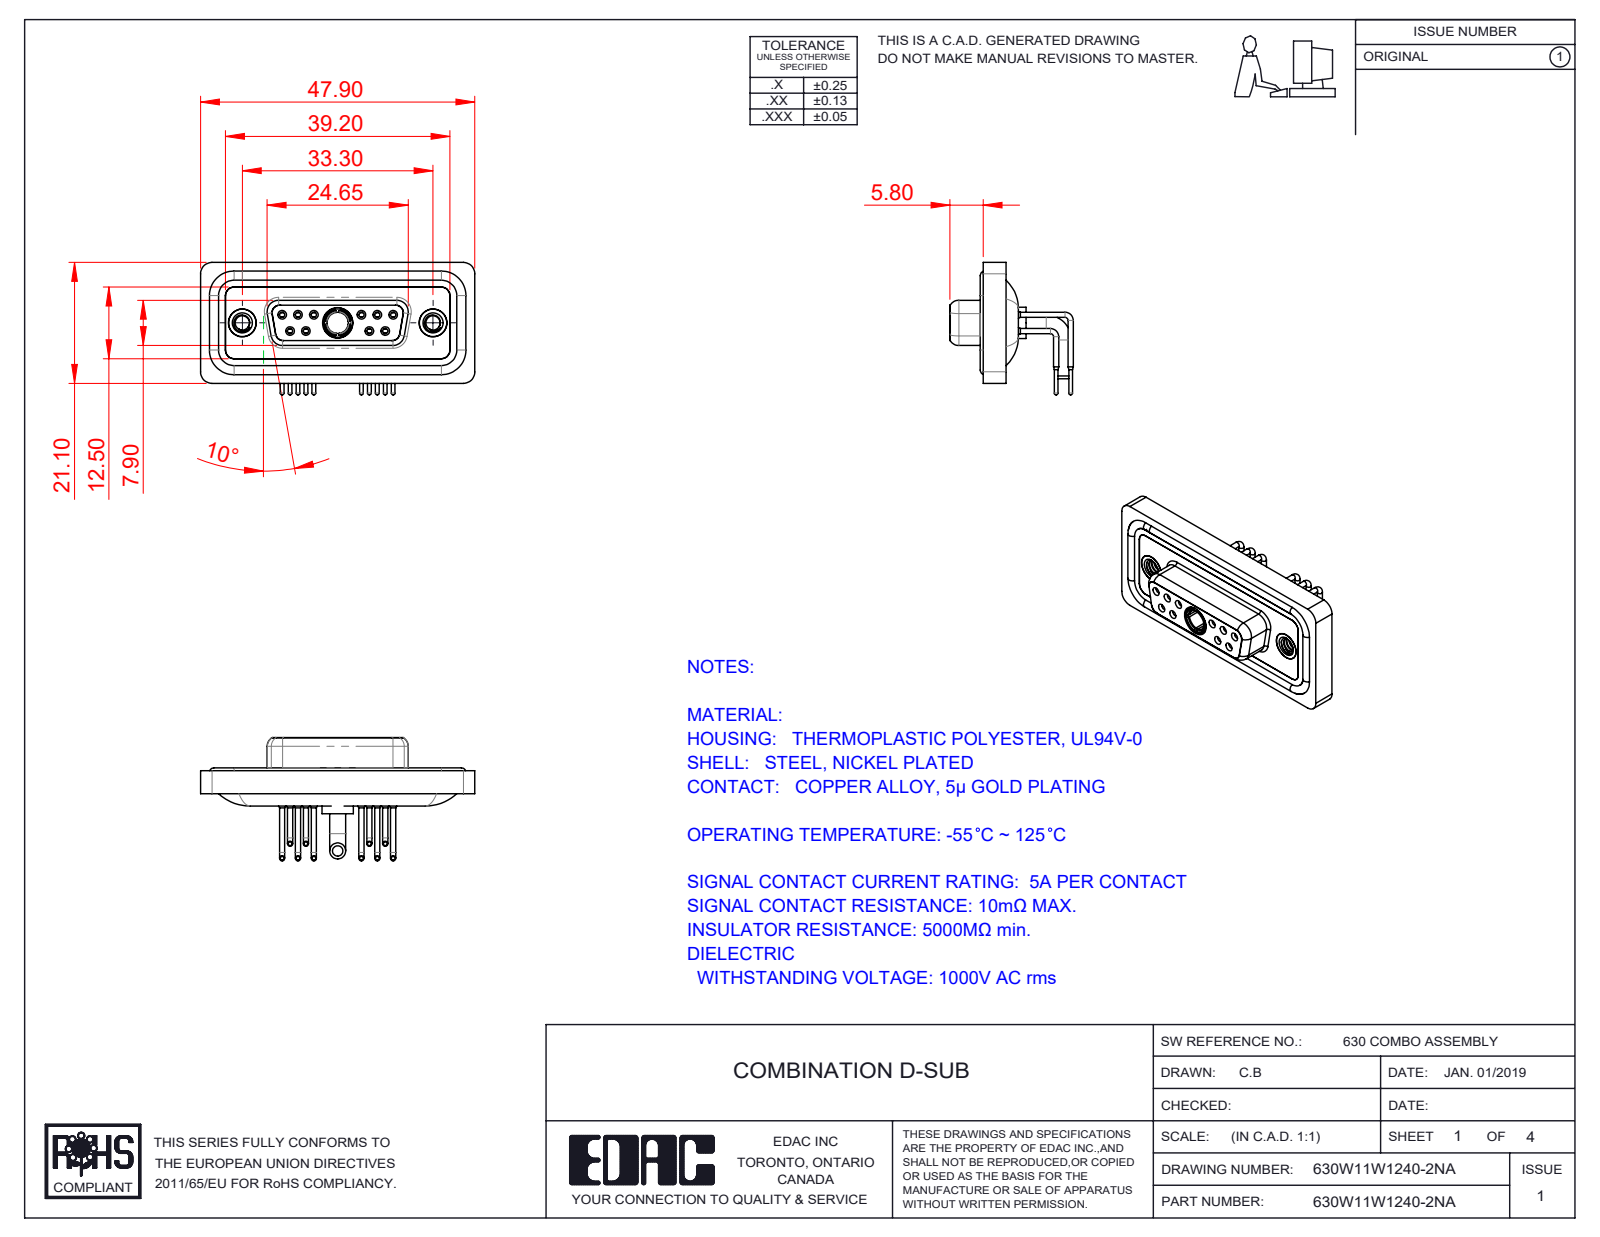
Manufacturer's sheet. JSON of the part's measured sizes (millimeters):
{"part_name": "630Combo Shell Front_15 Contacts; Power Socket_20A RA; 630W11W1240-2NA; 630Combo Shell Rear_15 Contacts (+5 more)", "step_written_by": "SolidWorks 2020 (CONFIG_CONTROL_DESIGN)", "units": "millimeters", "bodies": {"solids": 19, "faces": 988, "planar": 284, "cylindrical": 441, "other": 263}, "overall_size": [47.9, 23.12, 21.53], "volume_mm3": 6210, "surface_area_mm2": 10474, "round_holes": [[0.9, 10], [1.1, 10], [1.5, 10], [2, 10], [1.7, 6], [1.6, 4], [4.85, 3], [2.5, 2], [4, 2], [4.05, 2], [5, 2], [3.7, 1]], "round_bosses_or_shafts": [[1.6, 10], [0.9, 10], [0.65, 10], [4.95, 2], [4.8, 2], [2.8, 2], [5.5, 1], [5.2, 1]], "partial_cylinders_radius": [[2, 20], [1.5, 18], [1.35, 12], [1.6, 8], [0.25, 4], [0.5, 4], [0.6, 4], [0.65, 4]], "face_to_face_distances": [0.4, 1.8, 1.1, 1.6, 2.5, 2.9, 3.1, 3.7, 4.1, 1.5], "hole_center_spacings": [3.16, 2.77, 13.85, 11.08, 16.62, 5.03, 5.04, 5.54]}
